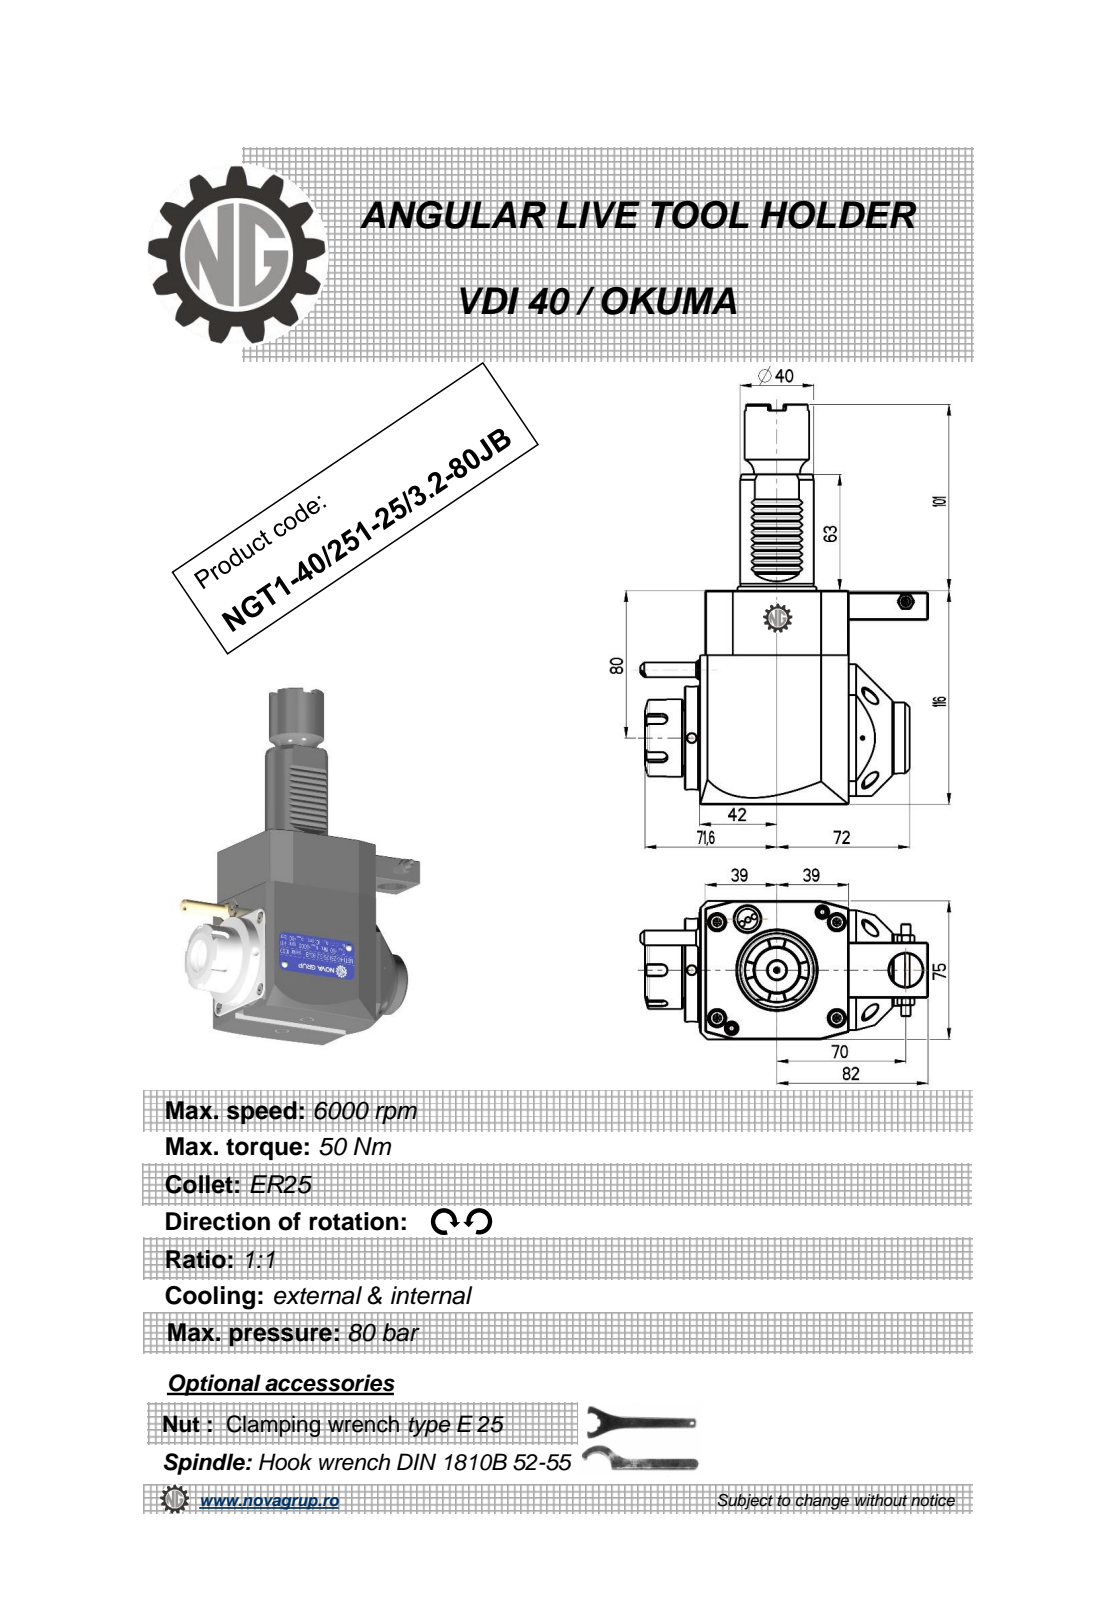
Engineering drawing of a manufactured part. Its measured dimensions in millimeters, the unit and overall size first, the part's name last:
Units: millimetres
Overall size (bounding box): 217 × 156.14 × 75
Round holes (diameter × count): ⌀5 ×3, ⌀3 ×1, ⌀4.2 ×1, ⌀9.5 ×1, ⌀18 ×1, ⌀20.3 ×1, ⌀25 ×1
Round bosses / shafts (diameter × count): ⌀56 ×1, ⌀43 ×1, ⌀42 ×1, ⌀40 ×1, ⌀38.5 ×1, ⌀35 ×1, ⌀33 ×1, ⌀10 ×1
Partial cylindrical surfaces — rounded edges, fillets, slot ends (radius × count): R0.26 ×12, R0.3 ×10, R0.2 ×6, R3 ×5, R0.5 ×1, R40 ×1
Main face-to-face distances: 75, 116, 81, 78, 3, 11, 8, 111, 1, 2.8
Hole centre spacings: 39.58, 40.93, 46.25, 70, 72.5, 116.25, 137.8
Volume: 930 548 mm³ · Surface area: 78 020 mm²
Bodies: 1 solid, 478 faces (203 planar, 89 cylindrical, 186 other)
Part name (STEP PRODUCT): NGT1_40_251_25_3_2_80JB
STEP written by: PRO/ENGINEER BY PARAMETRIC TECHNOLOGY CORPORATION, 2010280 (CONFIG_CONTROL_DESIGN)
